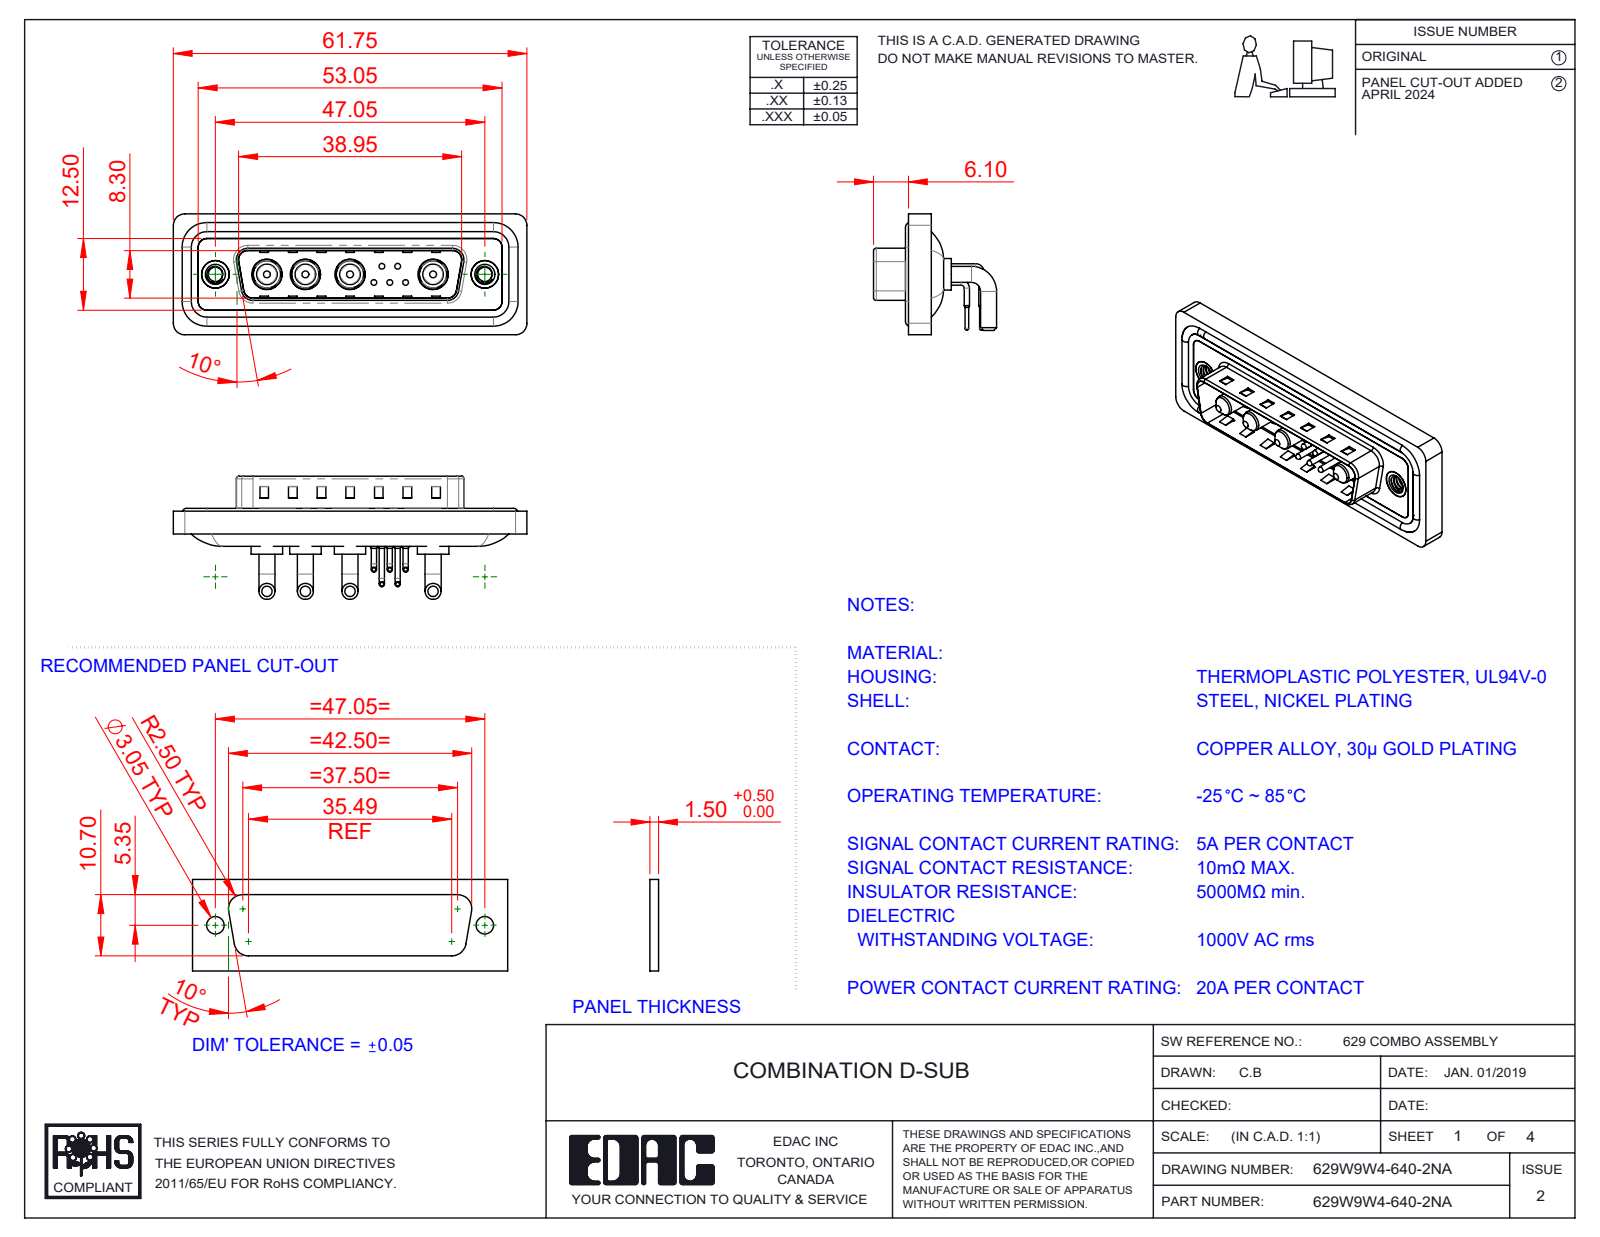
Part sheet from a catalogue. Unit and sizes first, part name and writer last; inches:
Units: inches
Overall size (bounding box): 2.431 × 0.846 × 0.831
Round holes (diameter × count): ⌀0.03 ×5, ⌀0.063 ×5, ⌀0.079 ×5, ⌀0.191 ×4, ⌀0.209 ×4, ⌀0.098 ×2, ⌀0.157 ×2, ⌀0.189 ×2, ⌀0.197 ×2
Round bosses / shafts (diameter × count): ⌀0.035 ×10, ⌀0.11 ×8, ⌀0.059 ×5, ⌀0.039 ×5, ⌀0.026 ×5, ⌀0.217 ×4, ⌀0.205 ×4, ⌀0.187 ×4
Partial cylindrical surfaces — rounded edges, fillets, slot ends (radius × count): R0.059 ×18, R0.079 ×18, R0.02 ×8, R0.063 ×8, R0.04 ×5, R0.01 ×4, R0.024 ×4, R0.026 ×4
Main face-to-face distances: 0.016, 0.114, 0.031, 0.161, 0.043, 0.177, 0.083, 0.063, 0.059, 0.122
Hole centre spacings: 0.124, 0.109, 0.198, 0.571, 0.109, 0.173, 0.174, 0.197
Volume: 0.47 in³ · Surface area: 19.19 in²
Bodies: 20 solids, 1199 faces (569 planar, 450 cylindrical, 180 other)
Part name (STEP PRODUCT): 629Combo Shell Rear_25 Contacts; 629Combo Threaded Rivet_A; 629Combo Contact Row 1; 629Combo Contact Row 2 (+5 more)
STEP written by: SolidWorks 2023 (CONFIG_CONTROL_DESIGN)
